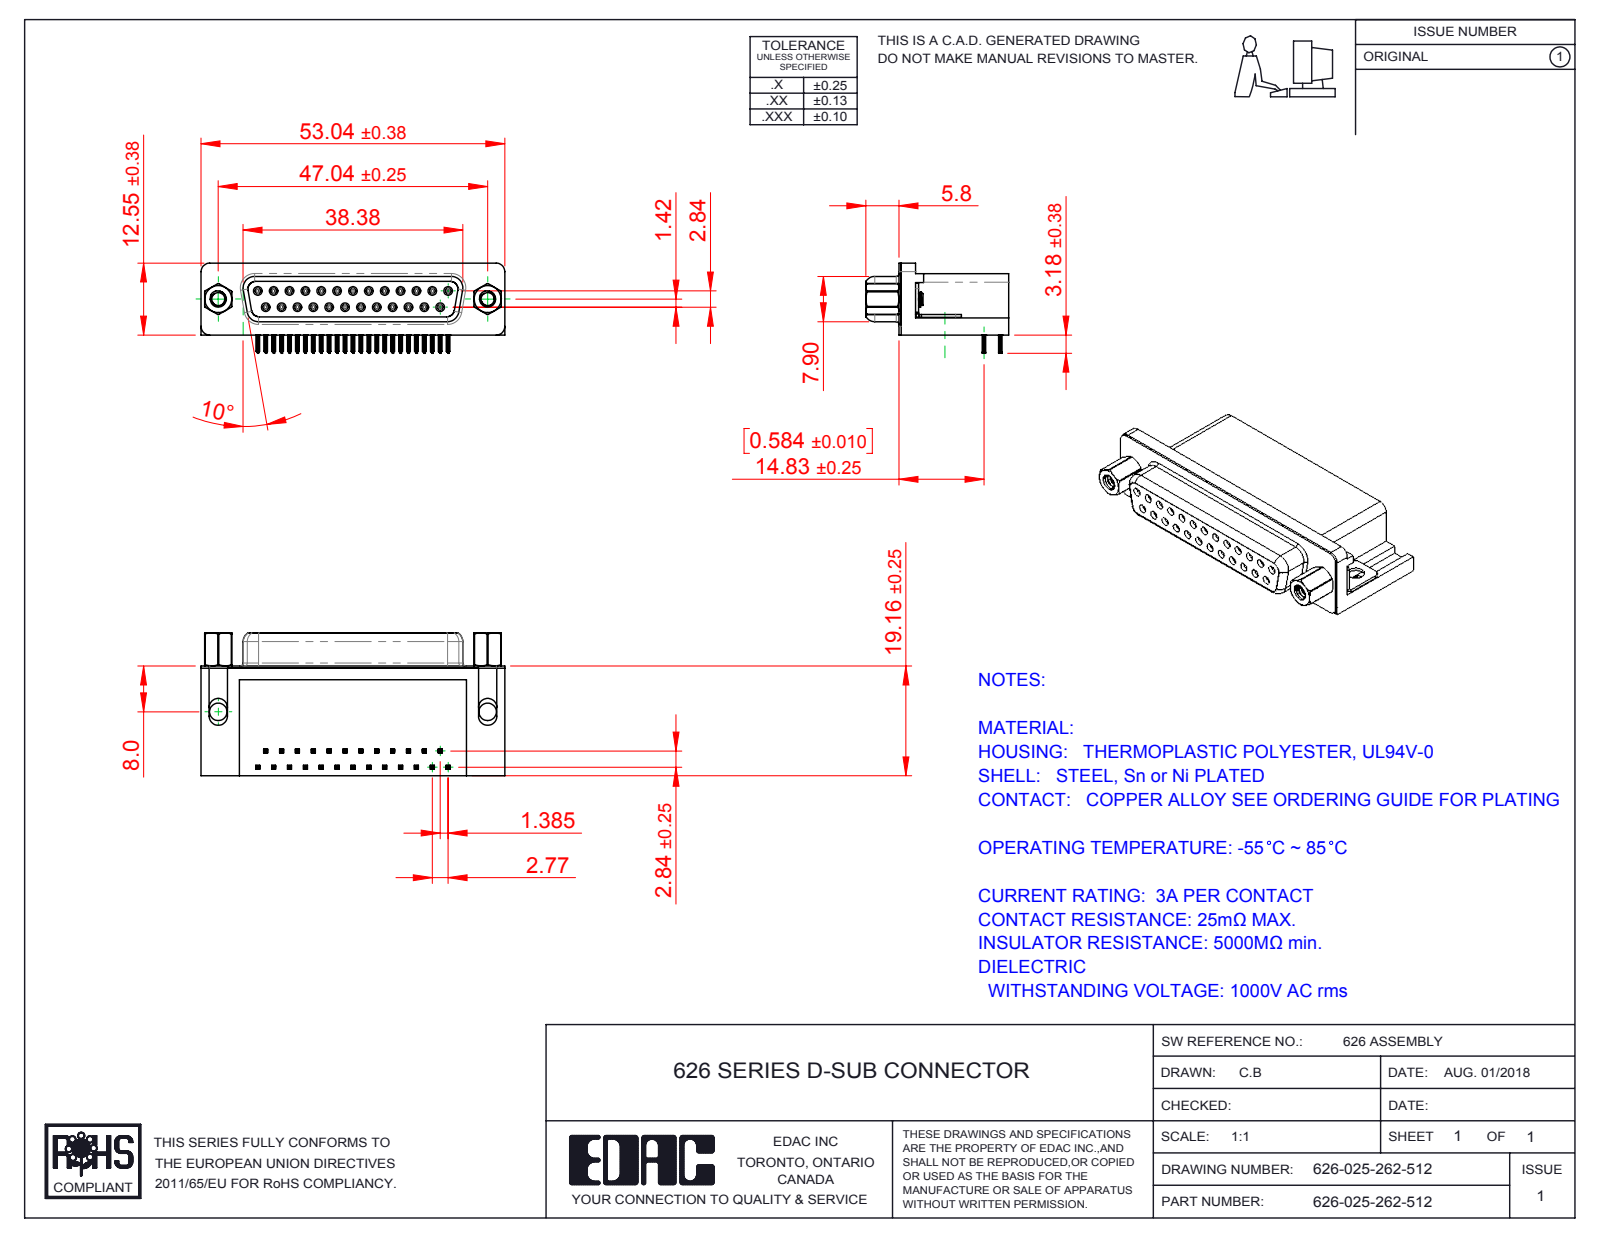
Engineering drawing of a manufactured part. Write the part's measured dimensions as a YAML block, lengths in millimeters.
part_name: "626-025-262-512; 626 Housing_25 Socket; 626 Contact Top; 626 Shell_25 Socket (+3 more)"
step_written_by: "SolidWorks 2016 (CONFIG_CONTROL_DESIGN)"
units: millimeters
bodies: {solids: 31, faces: 3888, planar: 1728, cylindrical: 954, other: 1206}
overall_size: [53.04, 24.96, 15.73]
volume: 10799
surface_area: 11514
round_holes:
  - {diameter: 0.8, count: 25}
  - {diameter: 0.9, count: 25}
  - {diameter: 2.29, count: 2}
  - {diameter: 3.05, count: 2}
  - {diameter: 4, count: 2}
  - {diameter: 4.8, count: 2}
  - {diameter: 5, count: 2}
round_bosses_or_shafts:
  - {diameter: 1.2, count: 25}
  - {diameter: 4.9, count: 2}
  - {diameter: 2.79, count: 2}
partial_cylinders:
  - {radius: 0.1, count: 200}
  - {radius: 0.15, count: 100}
  - {radius: 0.35, count: 50}
  - {radius: 0.34, count: 25}
  - {radius: 1, count: 18}
  - {radius: 0.28, count: 12}
  - {radius: 1.35, count: 8}
  - {radius: 1.6, count: 8}
face_to_face_distances: [0.4, 10.35, 18.76, 2.73, 6.2, 0.85, 9.38, 3.18, 2.84, 0.35]
hole_center_spacings: [3.16, 2.77, 5.54, 8.31, 11.08, 5.03, 5.04, 7.48]
